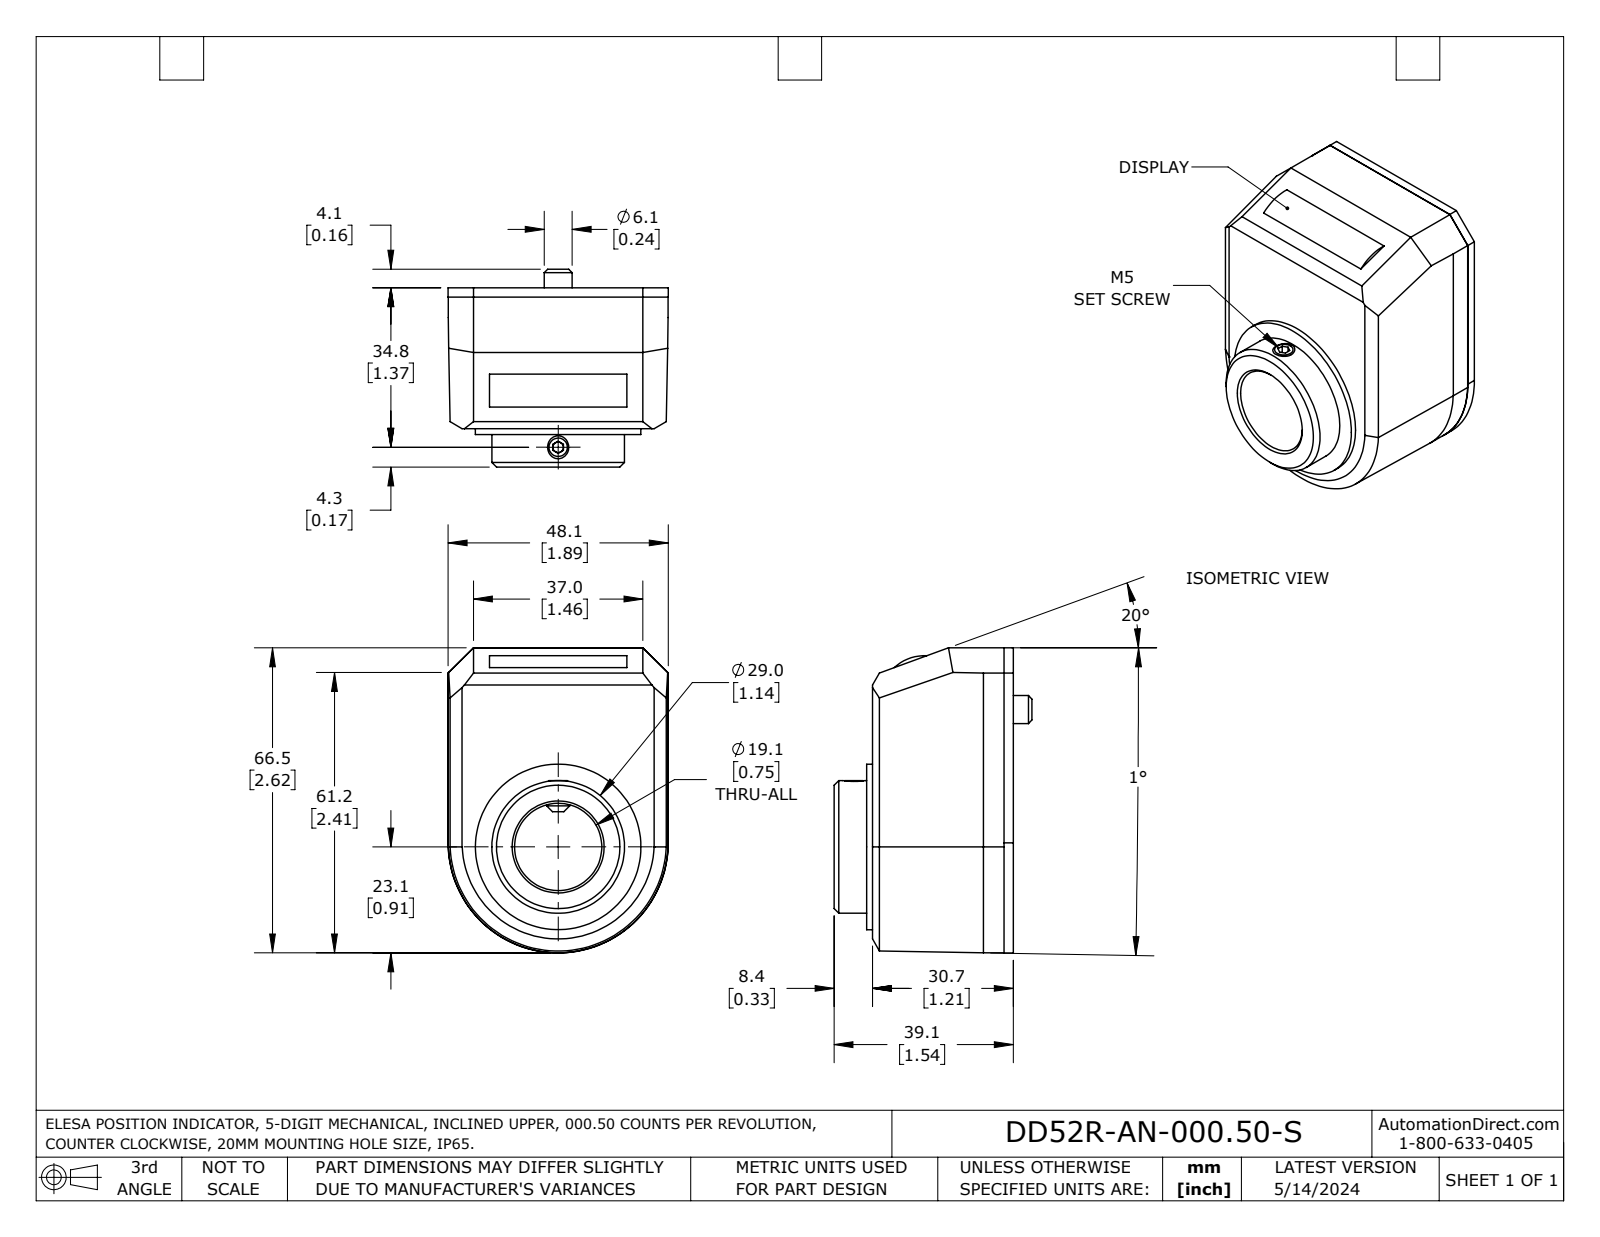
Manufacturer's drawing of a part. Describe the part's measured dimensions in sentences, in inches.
The part is named "DD52R-AN-METRIC". Its 3-D file was written by "SolidWorks 2023 (AUTOMOTIVE_DESIGN)". It is 3 solids with 68 faces: 46 planar, 13 cylindrical and 9 other. Overall it measures 2.622 by 1.892 by 1.7 inches. Its volume is 4.683 cubic inches and its surface area 28.91 square inches. Round holes: 1 of diameter 0.163, 1 of diameter 0.75, 1 of diameter 0.945, 1 of diameter 1.57, 1 of diameter 1.58. Round bosses or shafts: 1 of diameter 1.422, 1 of diameter 1.14, 1 of diameter 0.24, 1 of diameter 0.197. Partial cylindrical surfaces (rounded edges, fillets, slot ends): 1 of radius 0.39, 1 of radius 0.945, 1 of radius 0.946. The main face-to-face distances are 1.21, 1.051, 0.159, 0.05, 1.101, 1.26, 0.28, 0.33, 1.381, 1.54.
